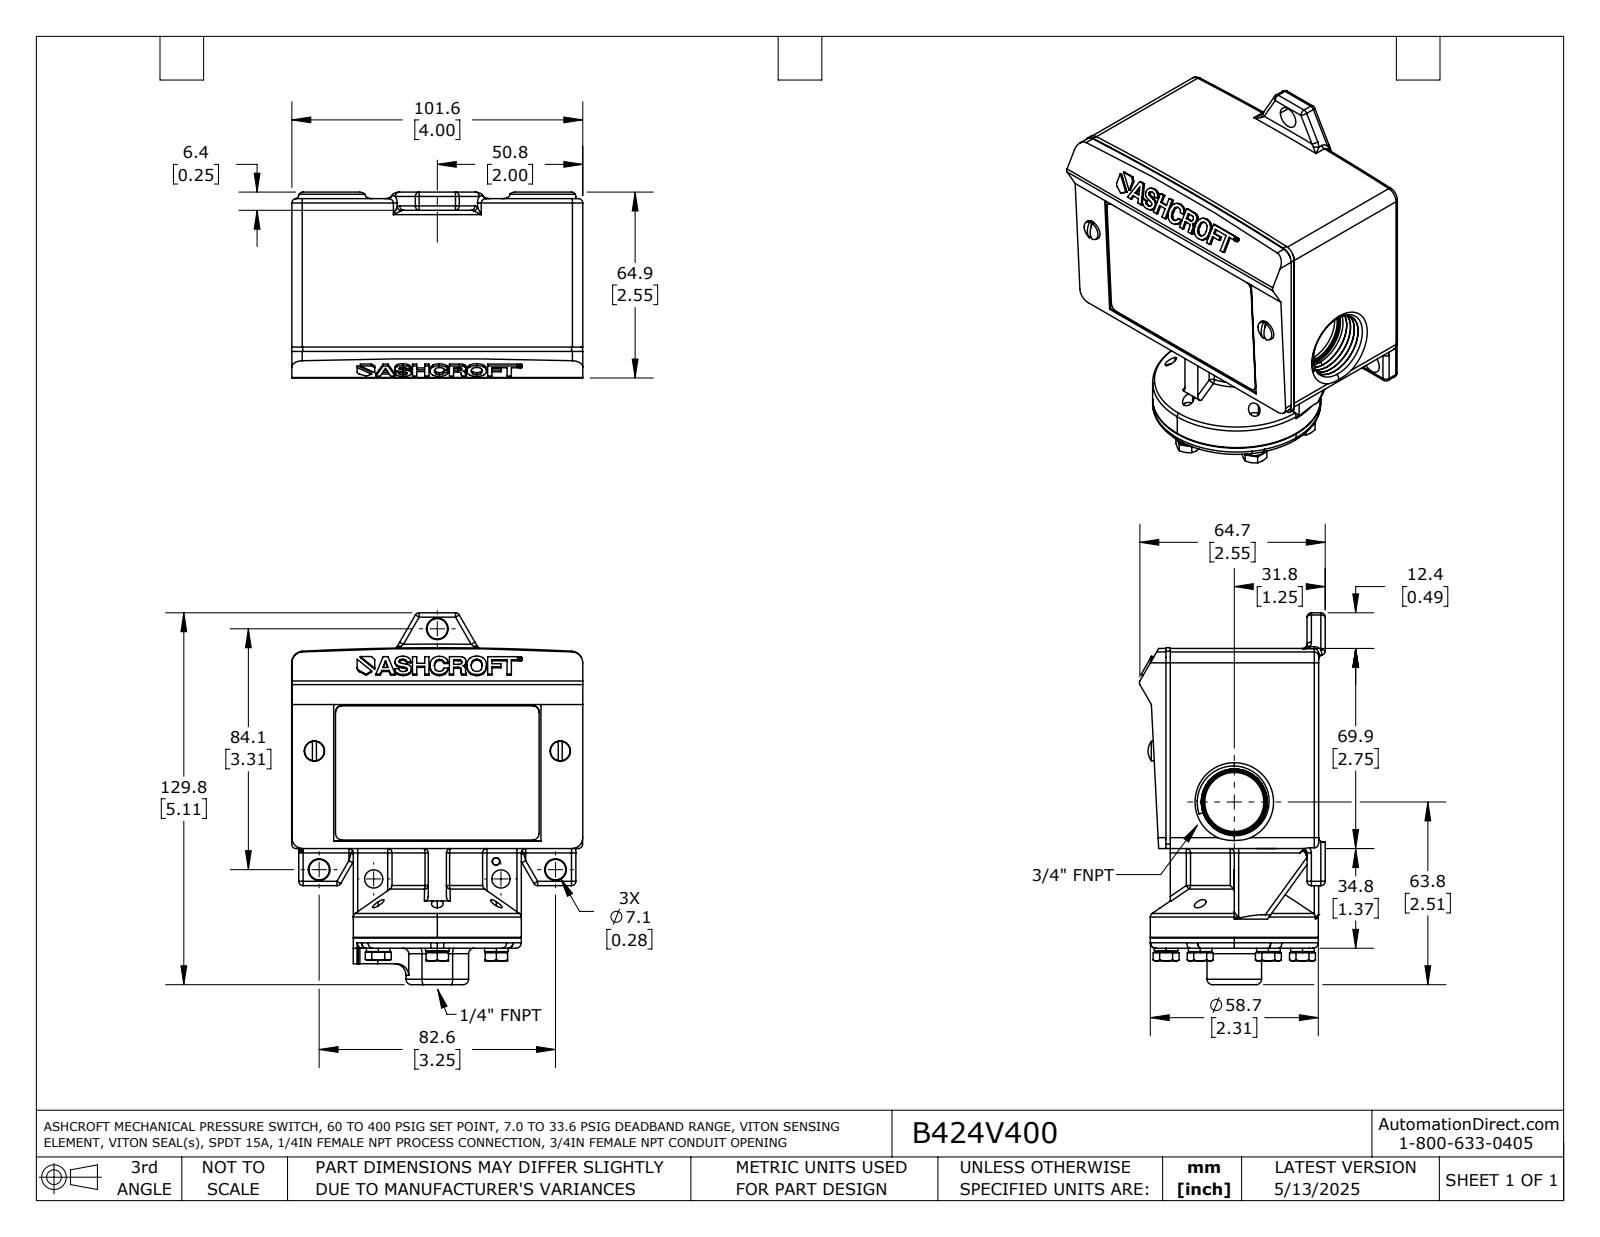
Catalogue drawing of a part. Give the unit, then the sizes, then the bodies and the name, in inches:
Units: inches
Overall size (bounding box): 5.111 × 4.003 × 2.555
Round holes (diameter × count): ⌀0.161 ×6, ⌀0.192 ×5, ⌀0.209 ×5, ⌀0.187 ×4, ⌀0.28 ×2, ⌀0.455 ×1, ⌀0.812 ×1
Round bosses / shafts (diameter × count): ⌀0.325 ×6, ⌀0.278 ×6, ⌀0.19 ×5, ⌀0.27 ×2, ⌀0.25 ×2, ⌀2.31 ×1
Partial cylindrical surfaces — rounded edges, fillets, slot ends (radius × count): R0.06 ×92, R0.03 ×5, R0.075 ×4, R0.09 ×4, R0.15 ×4, R0.01 ×2, R0.094 ×2, R0.16 ×2
Main face-to-face distances: 4, 0.015, 1.37, 0.09, 3.91, 0.44, 3.56, 3.47, 0.35, 0.845
Hole centre spacings: 0.937, 1.624, 1.875, 0.938, 3.38
Volume: 28.57 in³ · Surface area: 84.51 in²
Bodies: 2 solids, 1259 faces (345 planar, 472 cylindrical, 442 other)
Part name (STEP PRODUCT): B424V400
STEP written by: SolidWorks 2021 (AUTOMOTIVE_DESIGN)
